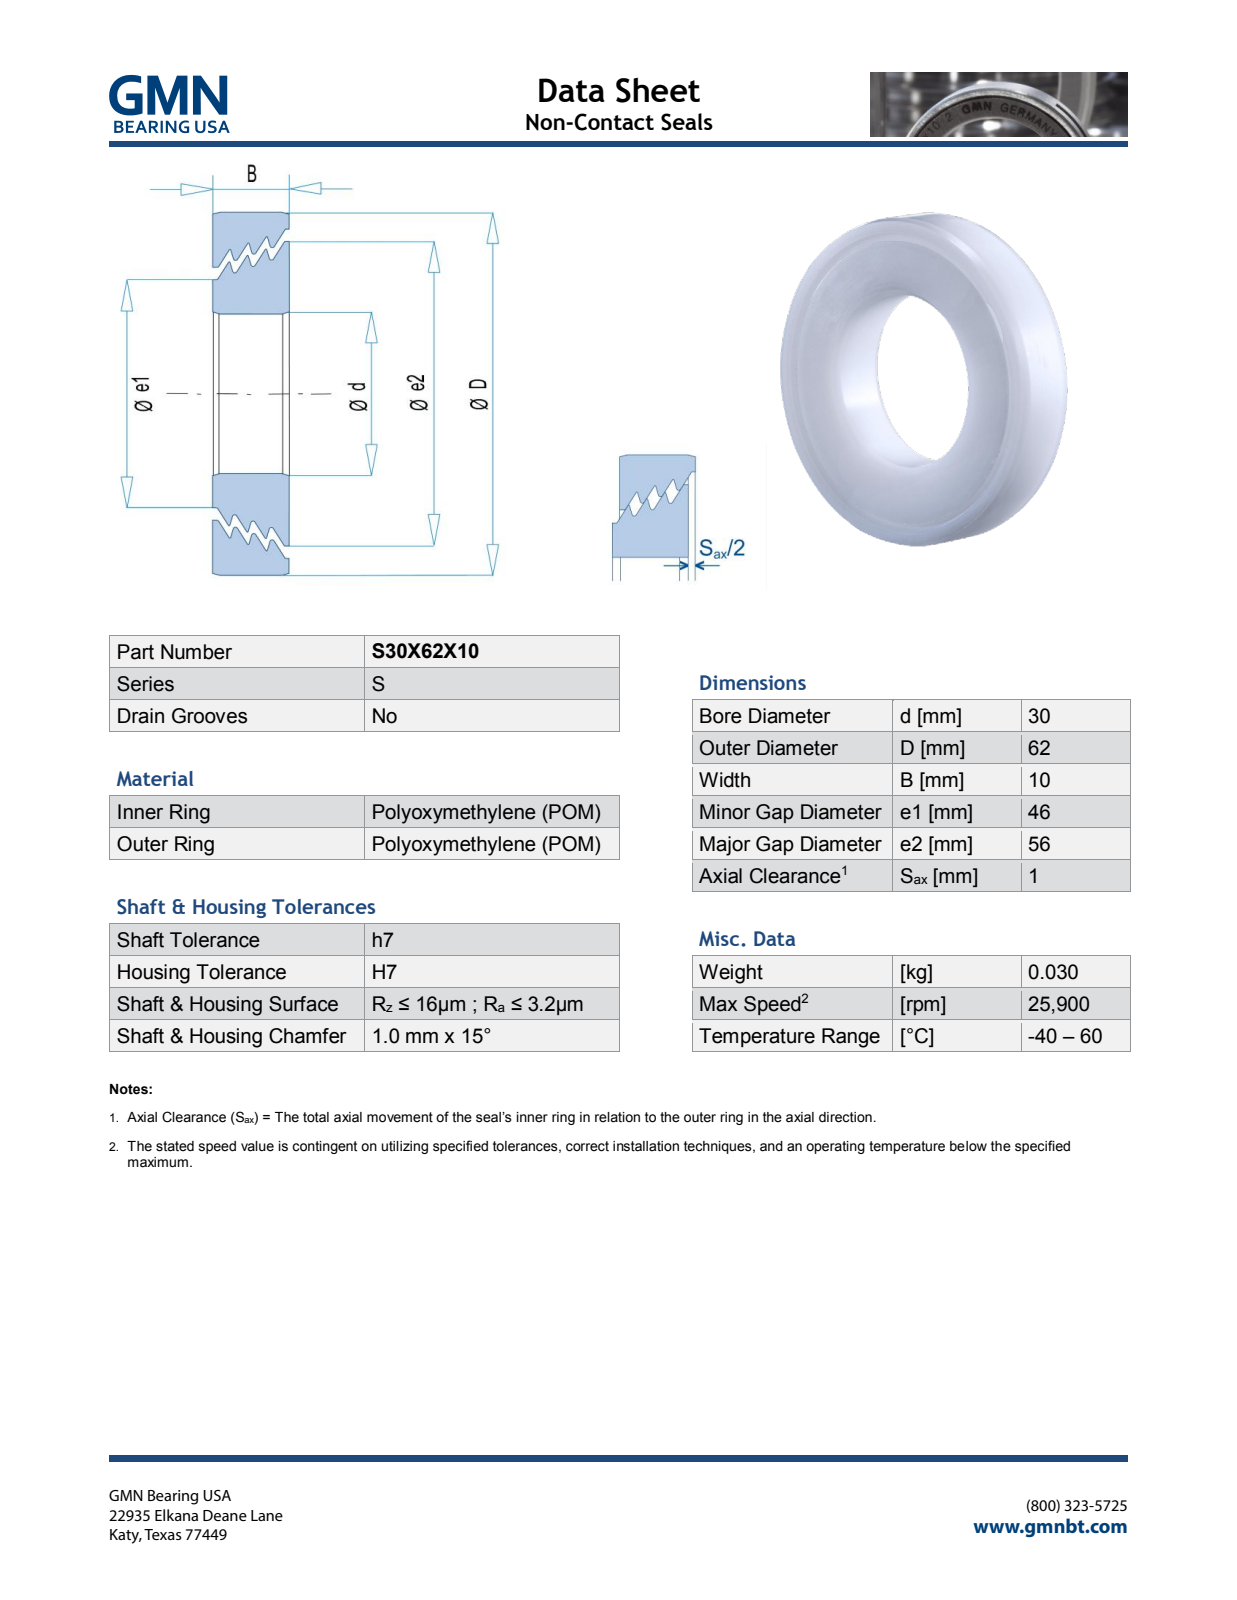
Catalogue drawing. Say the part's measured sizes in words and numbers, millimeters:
The part is named "S30X62X10_PRT". Its 3-D file was written by "PRO/ENGINEER BY PARAMETRIC TECHNOLOGY CORPORATION, 2013150 (AUTOMOTIVE_DESIGN)". It is 2 solids with 688 faces: 608 planar, 12 cylindrical and 68 other. Overall it measures 62 by 62 by 10.07 millimeters. Its volume is 21 723 cubic millimeters and its surface area 13 856 square millimeters. Round holes: 1 of diameter 30, 1 of diameter 47.63, 1 of diameter 57.63. Round bosses or shafts: 1 of diameter 62, 1 of diameter 56, 1 of diameter 46. The main face-to-face distances are 10, 10.07, 0.45, 0.46, 3.63, 3.18, 3.17, 3.64, 2.73, 0.38.
